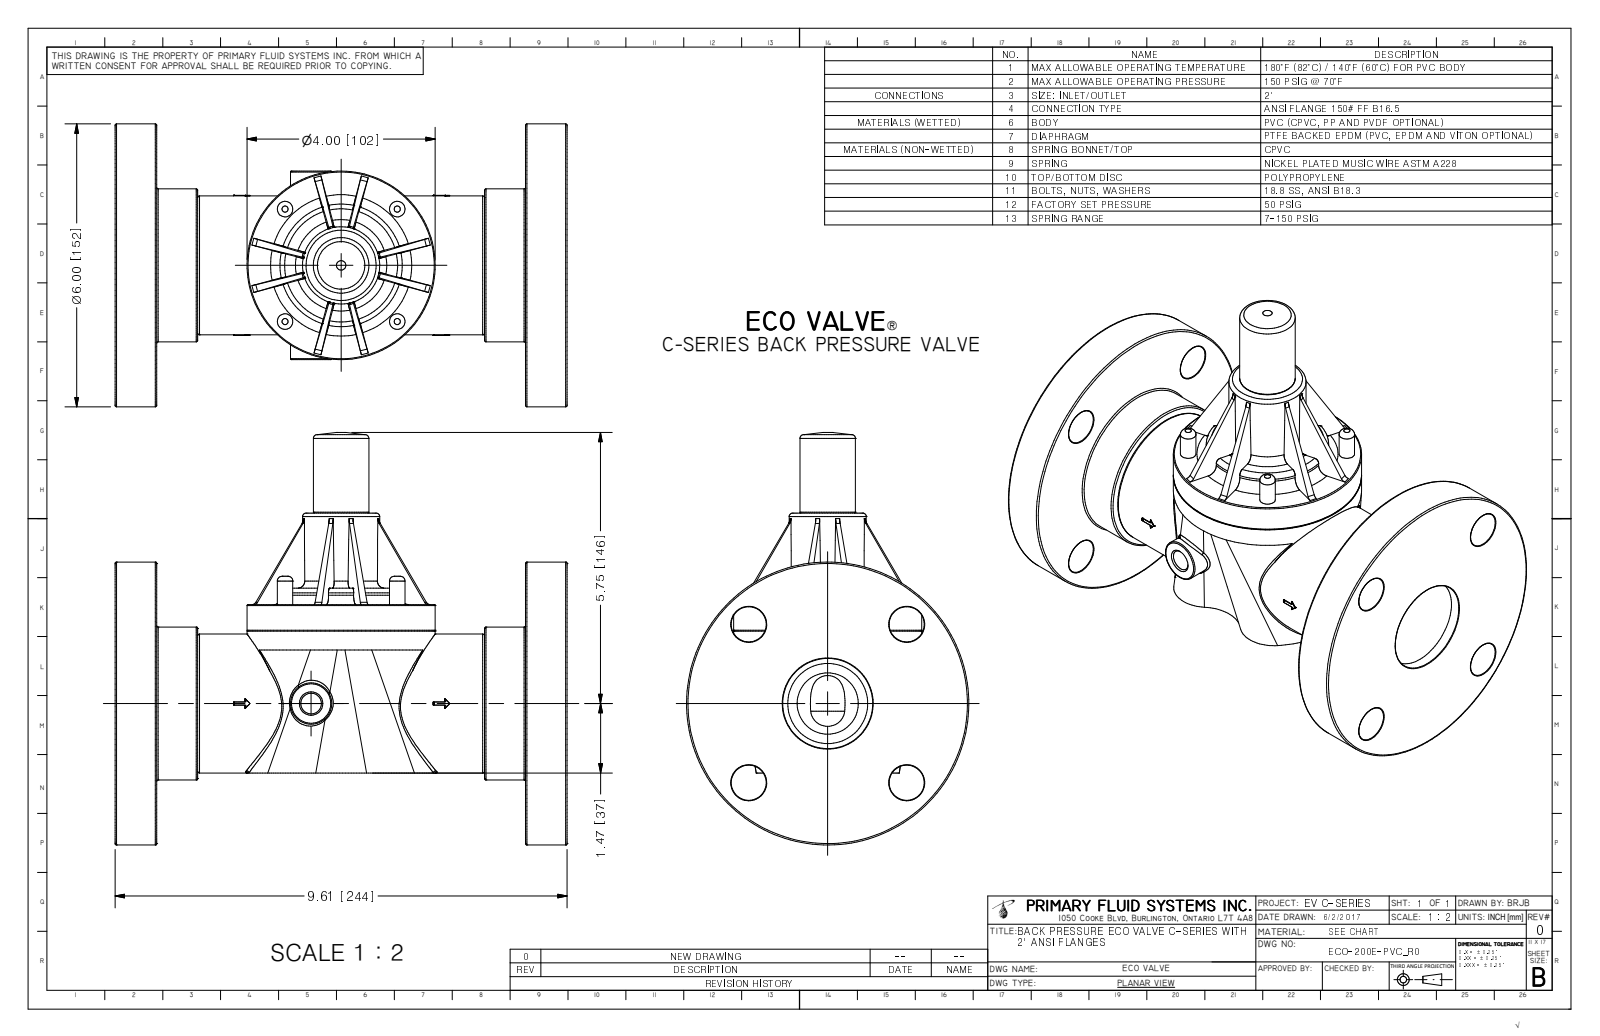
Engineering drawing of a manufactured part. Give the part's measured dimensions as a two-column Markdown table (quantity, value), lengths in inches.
| quantity | value |
| --- | --- |
| part name | ECO-200E-PVC_R0 |
| STEP written by | Autodesk Inventor 2009 (AUTOMOTIVE_DESIGN) |
| units | inches |
| bodies | 1 solid, 470 faces (179 planar, 103 cylindrical, 188 other) |
| overall size | 9.61 × 8.749 × 6 |
| volume | 105.1 in³ |
| surface area | 407 in² |
| round holes (diameter × count) | 0.23 × 4, 0.745 × 4, 0.437 × 1, 1.913 × 1, 1.939 × 1 |
| round bosses / shafts (diameter × count) | 0.4 × 4, 0.33 × 4, 6 × 1, 4 × 1, 3.244 × 1, 2.947 × 1, 2.6 × 1, 2.375 × 1 |
| partial cylindrical surfaces (radius × count) | 0.1 × 14, 0.05 × 4, 0.225 × 4, 0.15 × 1, 0.875 × 1, 1.484 × 1, 1.559 × 1, 1.816 × 1 |
| main face-to-face distances | 0.885, 8.725, 9.61, 7.84, 1.755, 7.855, 0.87, 6.97, 3.255, 6.355 |
| hole center spacings | 2.385, 2.375, 2.375, 3.359, 3.359, 3.373, 4.75 |
